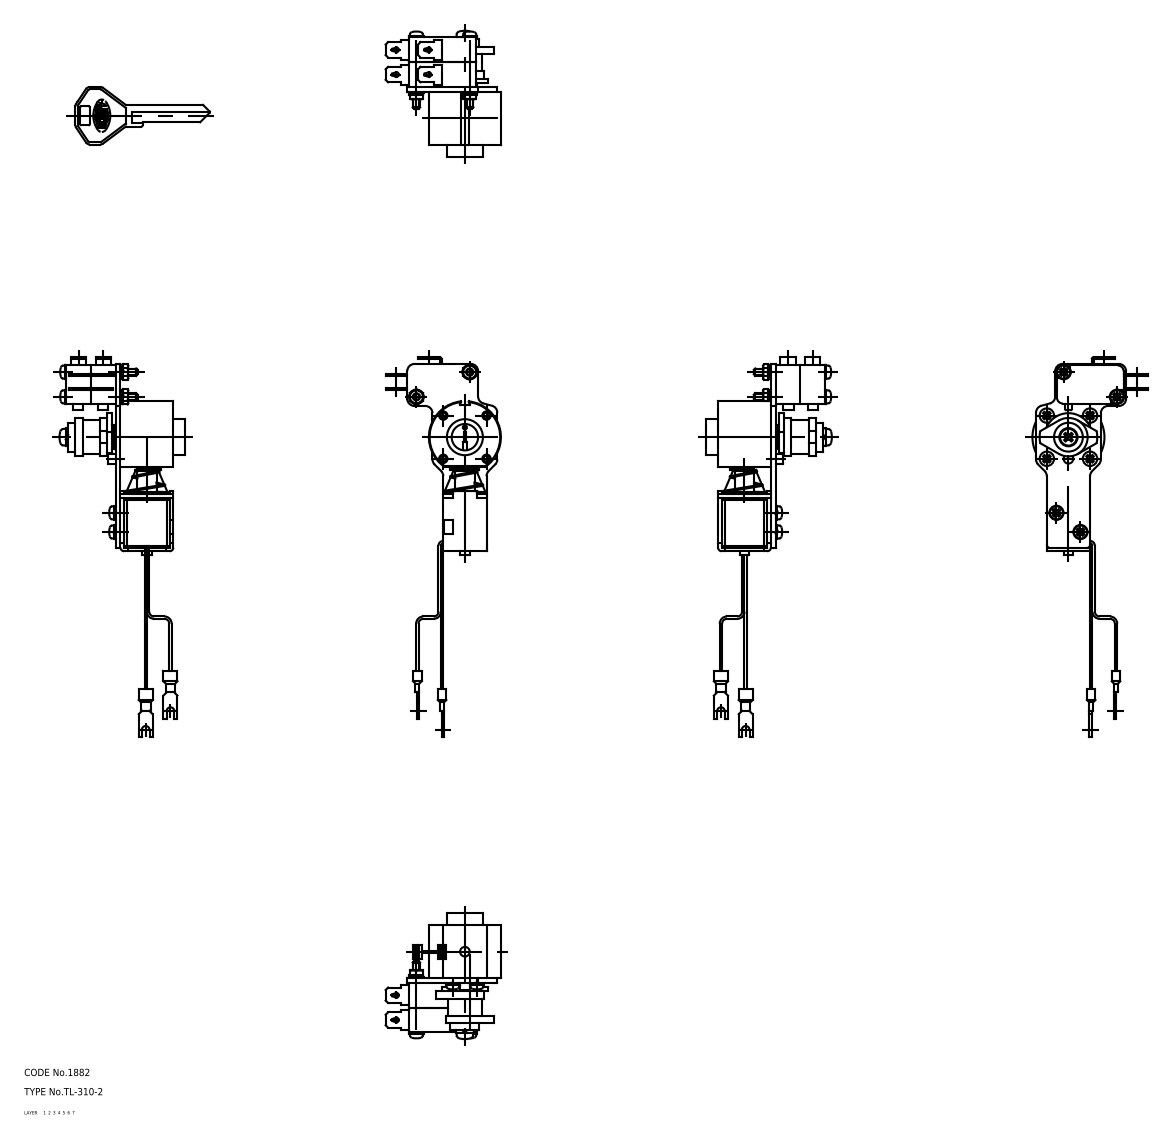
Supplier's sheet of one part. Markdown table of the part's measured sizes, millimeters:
| quantity | value |
| --- | --- |
| part name | spring; screw_3; screw_4; nut (+8 more) |
| STEP written by | CADfix (AUTOMOTIVE_DESIGN) |
| units | millimeters |
| bodies | 24 solids, 816 faces (0 planar, 0 cylindrical, 816 other) |
| overall size | 153.78 × 141.84 × 48 |
| volume | 41 087 mm³ |
| surface area | 26 061 mm² |
